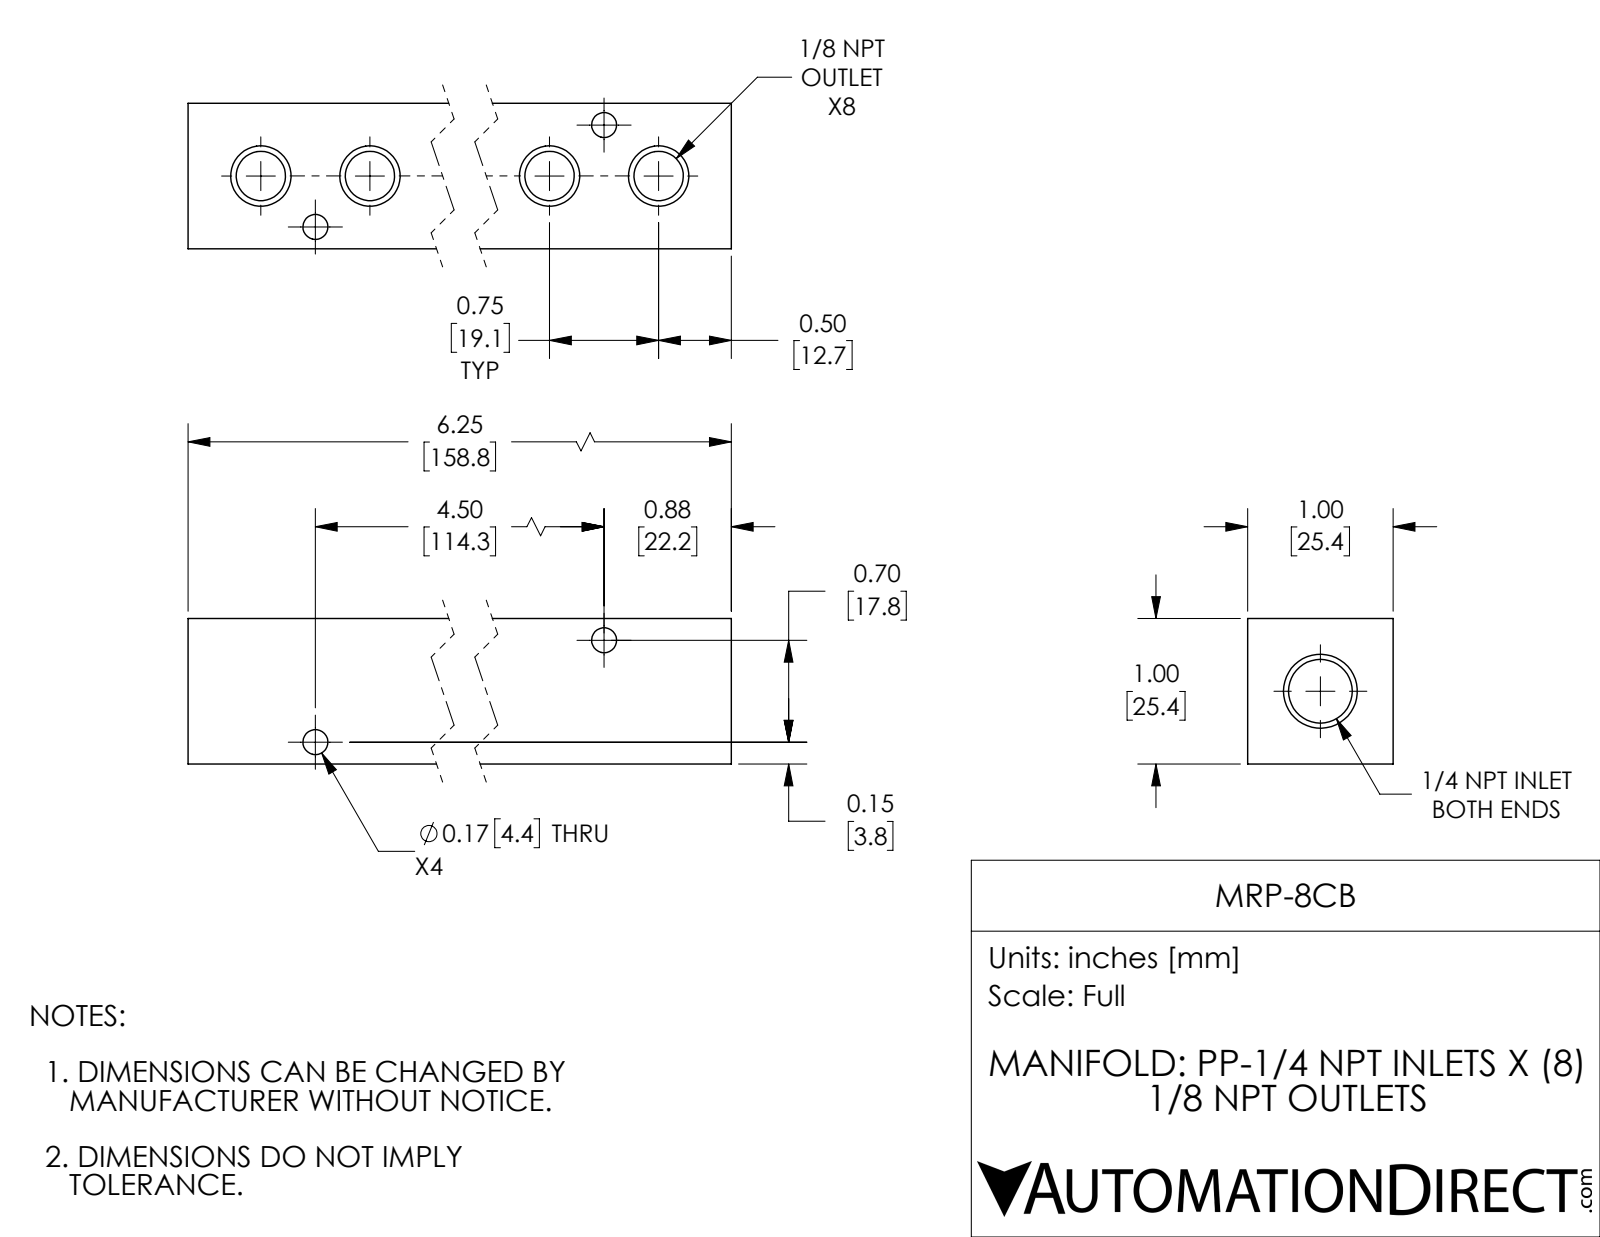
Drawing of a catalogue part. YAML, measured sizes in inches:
part_name: "MRP-8CB"
step_written_by: "SolidWorks 2018 (AUTOMOTIVE_DESIGN)"
units: inches
bodies: {solids: 1, faces: 60, planar: 6, cylindrical: 34, other: 20}
overall_size: [6.25, 1, 1]
volume: 4.998
surface_area: 38.01
round_holes:
  - {diameter: 0.339, count: 8}
  - {diameter: 0.172, count: 4}
  - {diameter: 0.438, count: 1}
face_to_face_distances: [1, 6.25]
hole_center_spacings: [0.75, 1.5, 2.25, 0.513, 3, 3.75, 1.178, 1.907]
